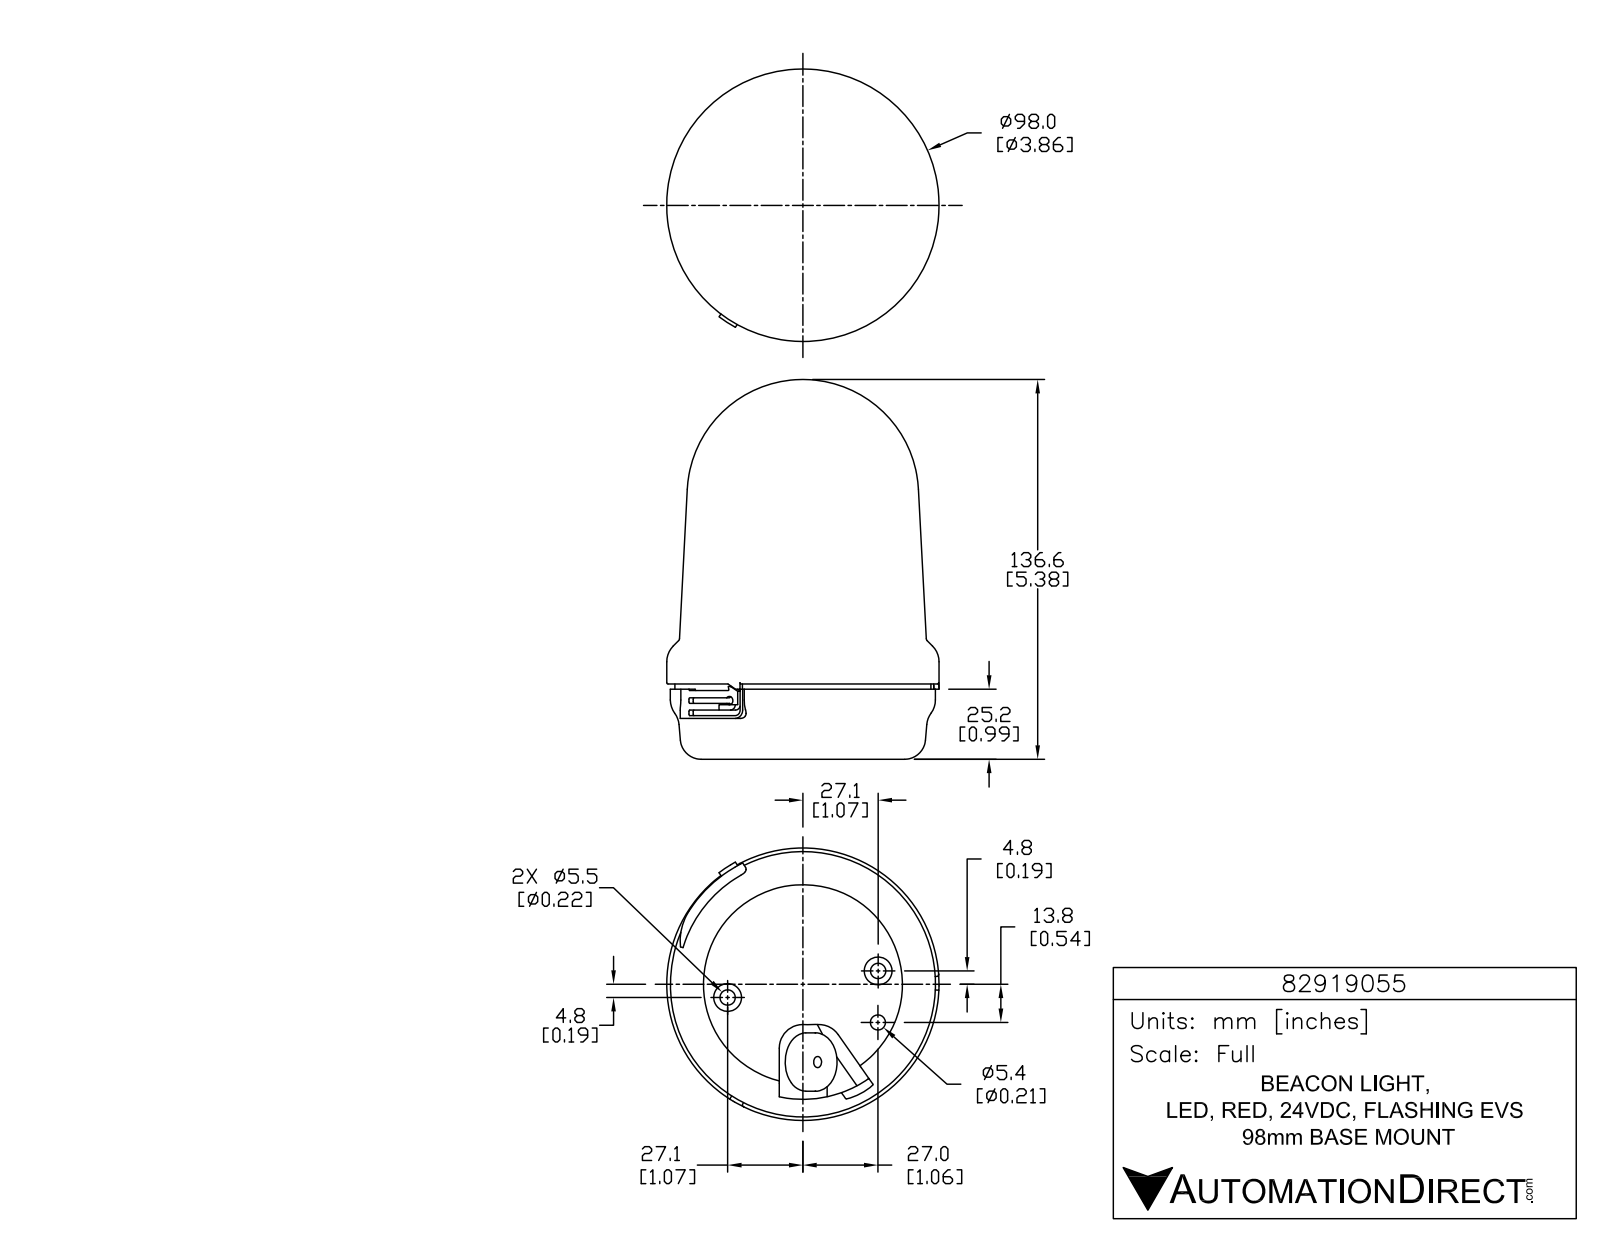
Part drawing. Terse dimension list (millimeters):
name: 82919055
written by: SolidWorks 2015 (AUTOMOTIVE_DESIGN)
unit: mm
bodies: 1 solid, 872 faces (566 planar, 204 cylindrical, 102 other)
size: 136.6 × 98 × 98
volume: 732 300 mm³; area: 47 520 mm²
holes: 3× ⌀1.5, 2× ⌀5.5, 1× ⌀4, 1× ⌀5.4, 1× ⌀71.6
bosses: 3× ⌀8.6, 3× ⌀2.1, 2× ⌀10, 1× ⌀98, 1× ⌀95.4, 1× ⌀92.1, 1× ⌀21
rounds: 9× R0.1, 6× R0.1, 6× R0.3, 6× R0.3, 6× R0.3, 6× R5, 5× R0.5, 4× R1
face distances: 26.5, 24.7, 1.9, 0.5, 25.2, 27.1, 6, 14.7, 14.2, 10.5
hole spacings: 27.5, 18.5, 30.3, 54.8, 55
